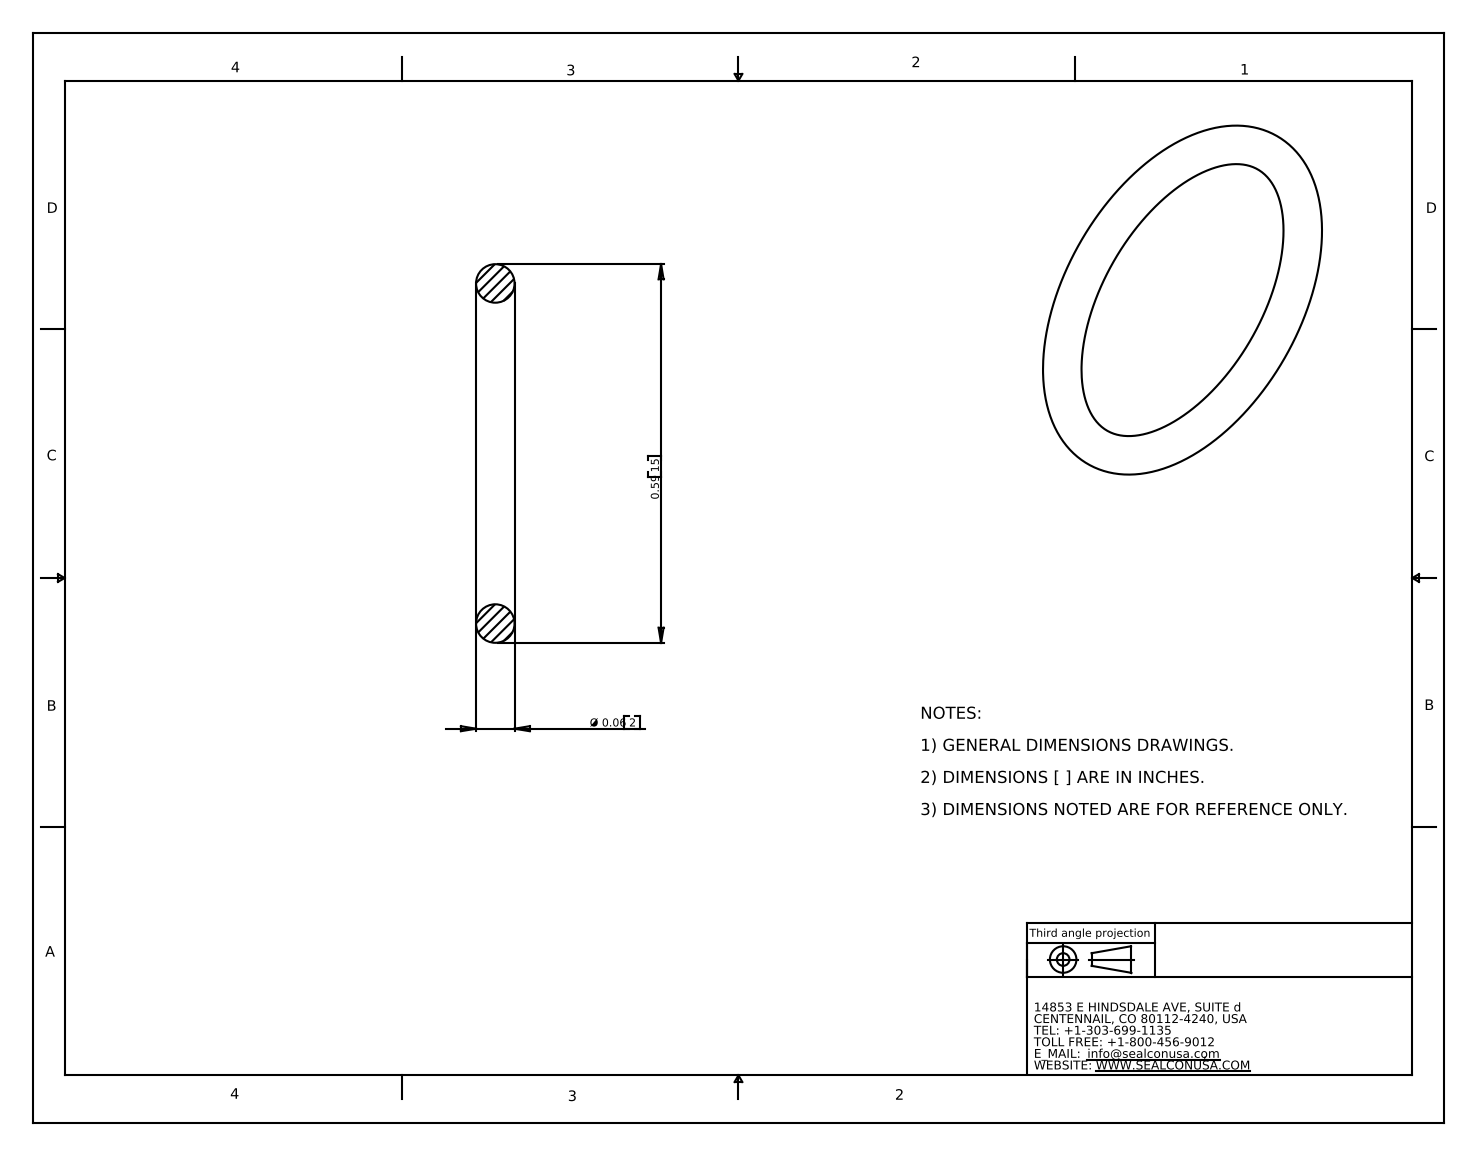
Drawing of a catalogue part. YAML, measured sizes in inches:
part_name: "OR-09-VT"
step_written_by: "SolidWorks 2007 (CONFIG_CONTROL_DESIGN)"
units: inches
bodies: {solids: 1, faces: 4, planar: 0, cylindrical: 0, other: 4}
overall_size: [0.59, 0.59, 0.06]
volume: 0.005
surface_area: 0.314
